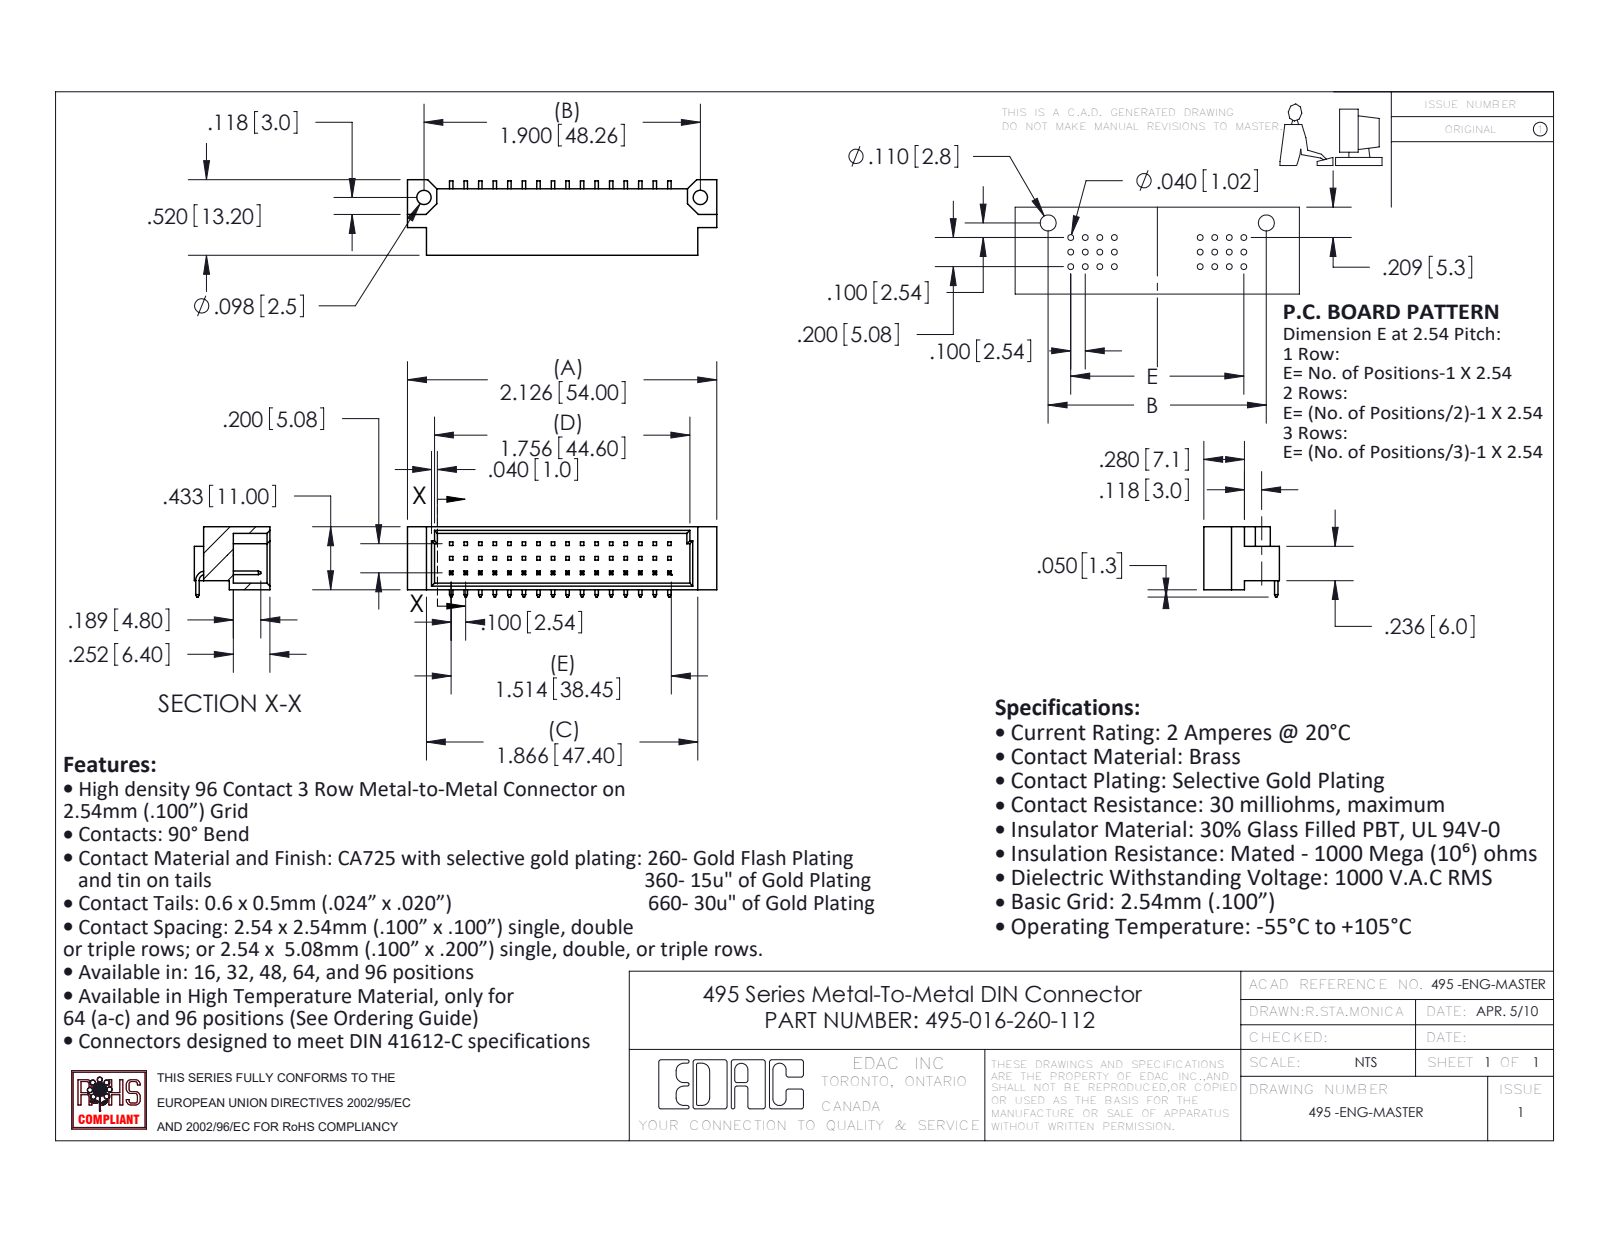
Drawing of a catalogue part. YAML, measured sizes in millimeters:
part_name: "495-016-260-112; 495 Part_48; 495-290-3"
step_written_by: "SolidWorks 2020 (AUTOMOTIVE_DESIGN)"
units: millimeters
bodies: {solids: 17, faces: 530, planar: 494, cylindrical: 36, other: 0}
overall_size: [54, 13.2, 12.27]
volume: 3535
surface_area: 4531
round_holes:
  - {diameter: 2.49, count: 2}
partial_cylinders:
  - {radius: 1.02, count: 1}
  - {radius: 1.65, count: 1}
face_to_face_distances: [1.14, 9.86, 5.2, 2.54, 11, 1.6, 5.08, 0.61, 8.72, 9.4]
hole_center_spacings: [48.26]
